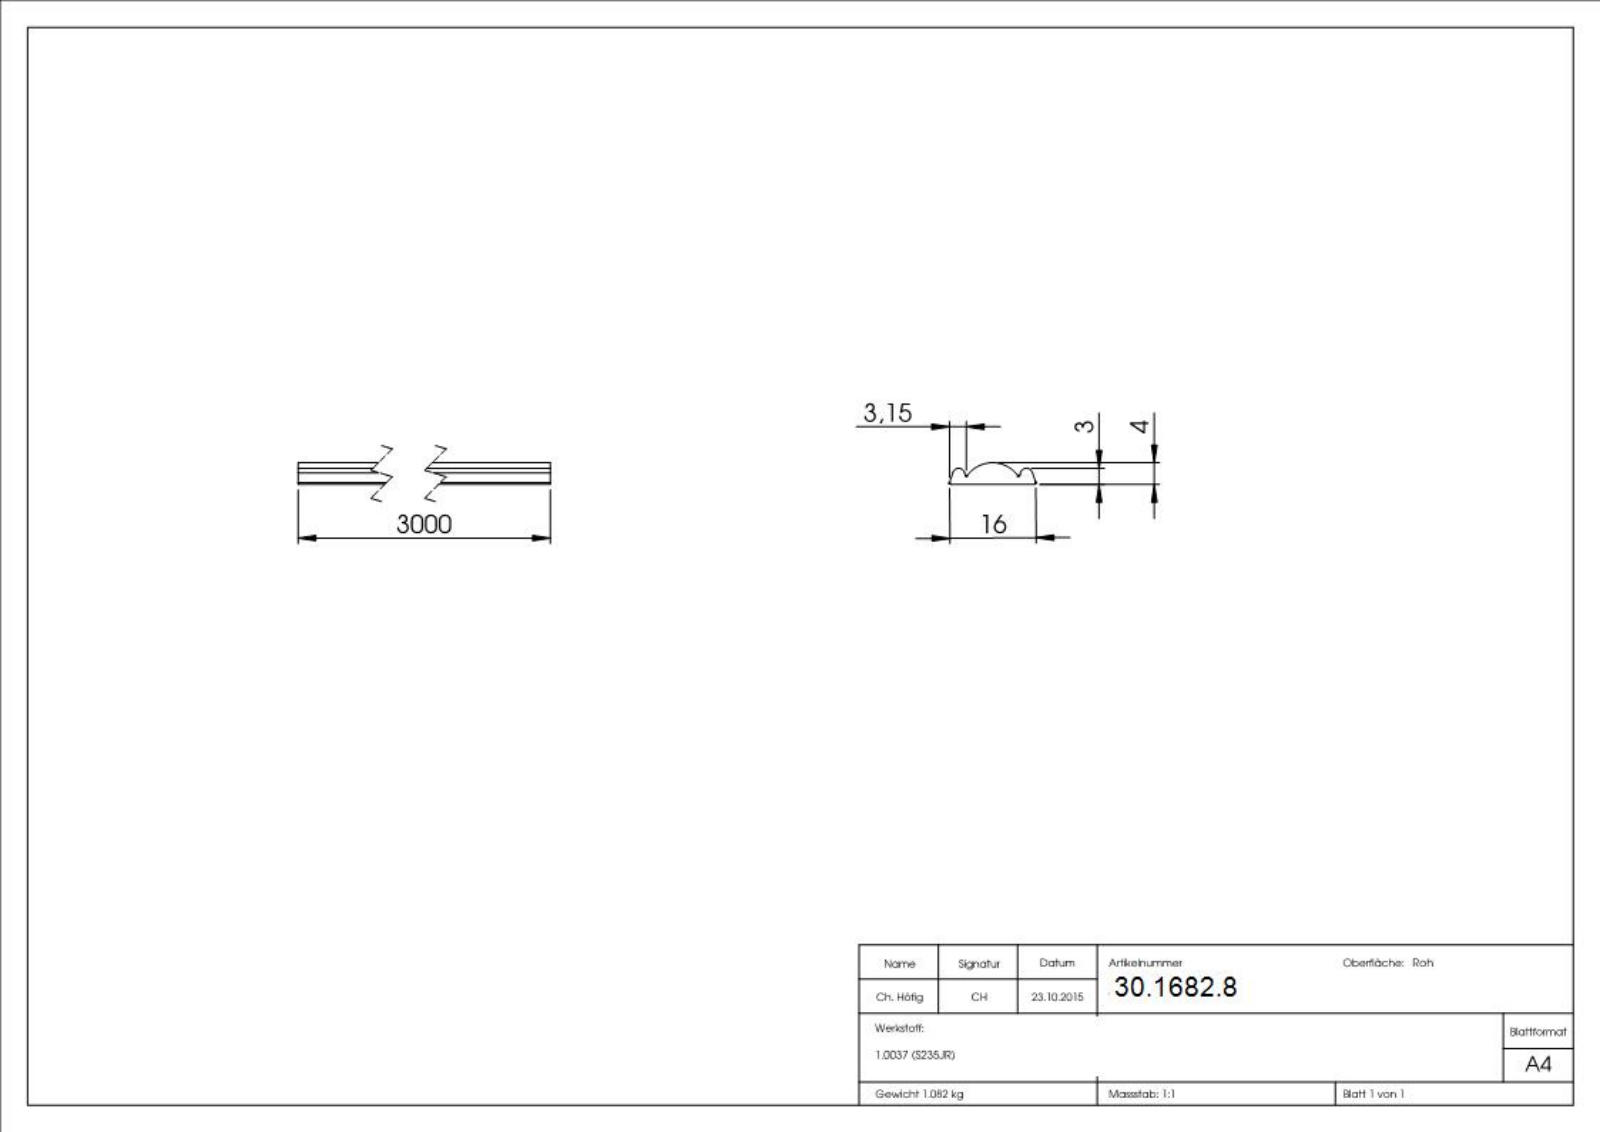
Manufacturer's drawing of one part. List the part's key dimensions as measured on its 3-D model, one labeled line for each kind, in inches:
Part name (STEP PRODUCT): 6303
STEP written by: SolidWorks 2015 (CONFIG_CONTROL_DESIGN)
Units: inches
Bodies: 1 solid, 190 faces (85 planar, 11 cylindrical, 94 other)
Overall size (bounding box): 118.11 × 0.622 × 0.157
Volume: 8.35 in³ · Surface area: 178.8 in²
Partial cylindrical surfaces — rounded edges, fillets, slot ends (radius × count): R0.01 ×4, R0.049 ×4, R0.223 ×1
Main face-to-face distances: 118.11, 0.015, 0.044, 0.08, 0.05, 0.065, 0.117, 0.129, 0.052, 0.144
